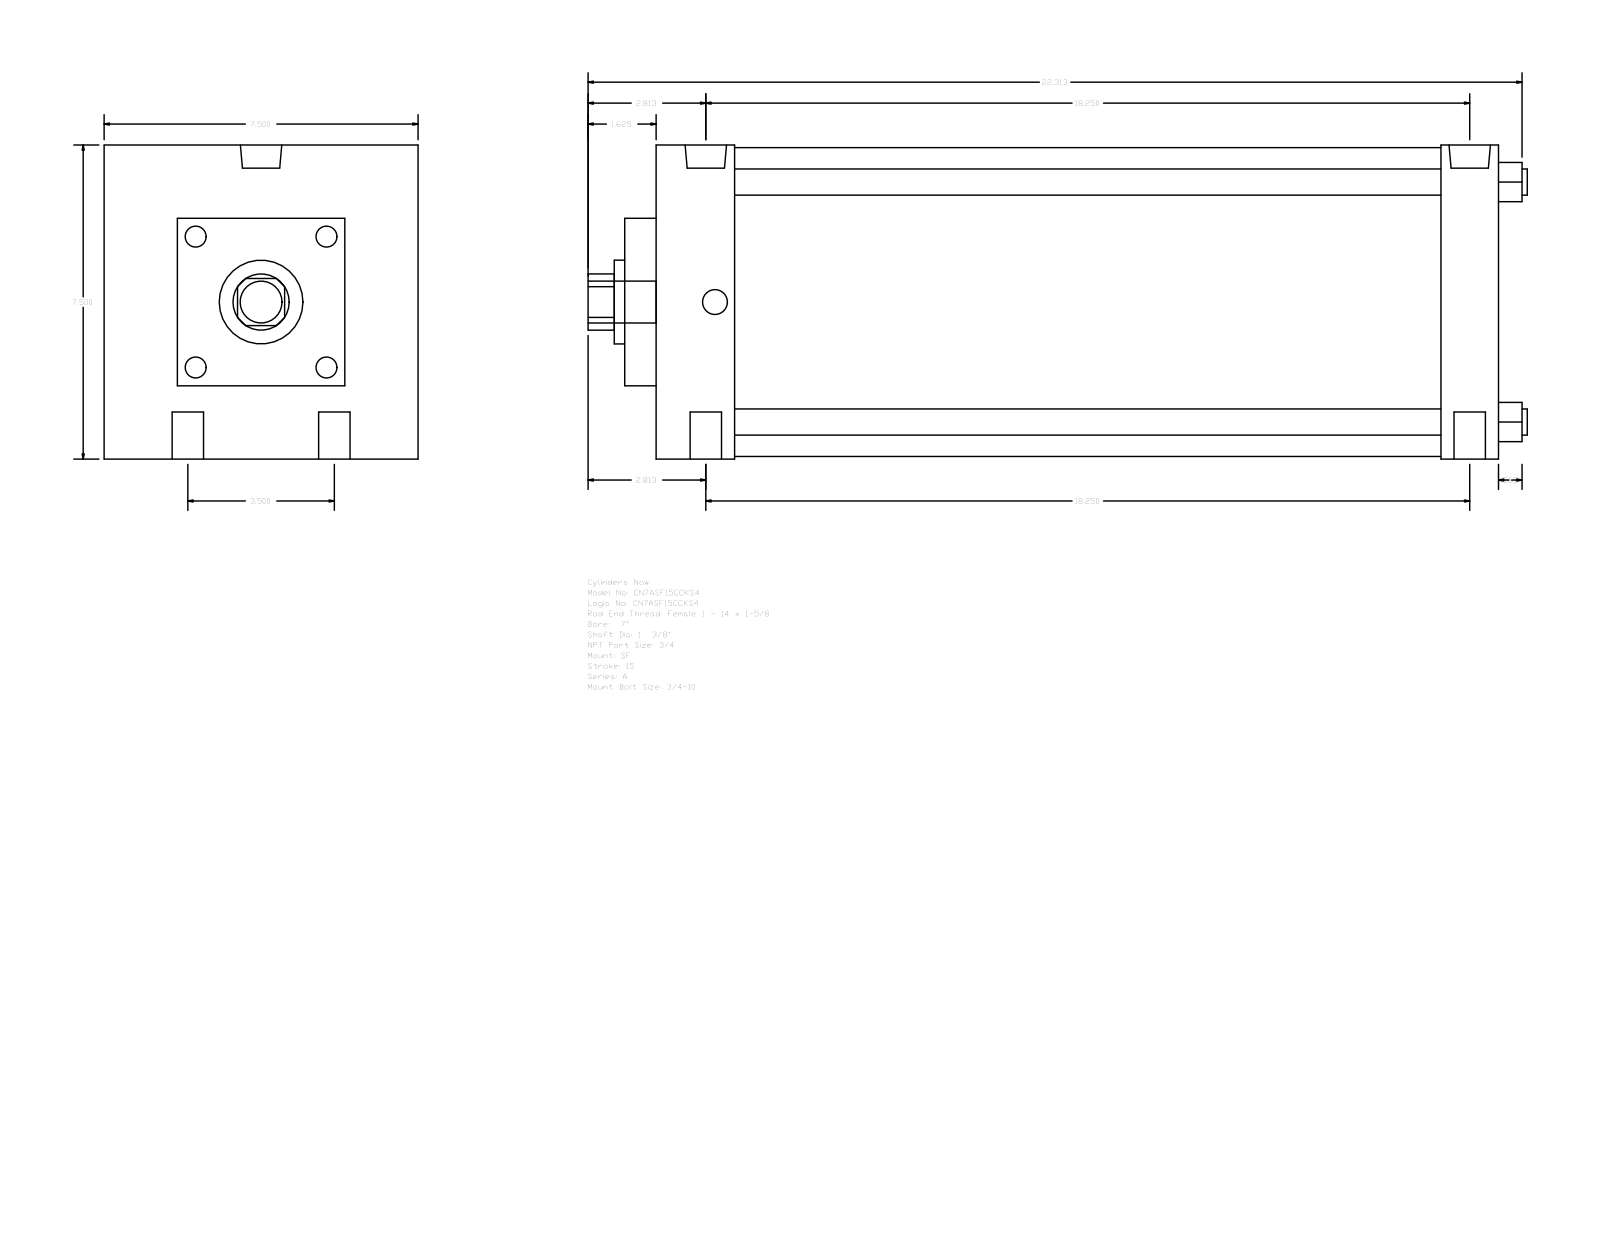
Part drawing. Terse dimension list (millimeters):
name: A_SF__0700_1.375
written by: GSSL Pune (CONFIG_CONTROL_DESIGN)
unit: mm
bodies: 0 solids, 93 faces (67 planar, 26 cylindrical, 0 other)
size: 569.91 × 190.5 × 190.5
holes: 4× ⌀19.05, 2× ⌀15.08, 2× ⌀25.12, 1× ⌀34.92, 1× ⌀50.8
bosses: 4× ⌀15.88, 1× ⌀187.32, 1× ⌀25.4
rounds: 1× R17.06
face distances: 190.5, 511.18, 19.04, 530.22, 66.67, 495.29, 47.63, 476.25, 428.62, 463.55
hole spacings: 44.45, 465.68, 463.55, 88.9, 472, 452.43
